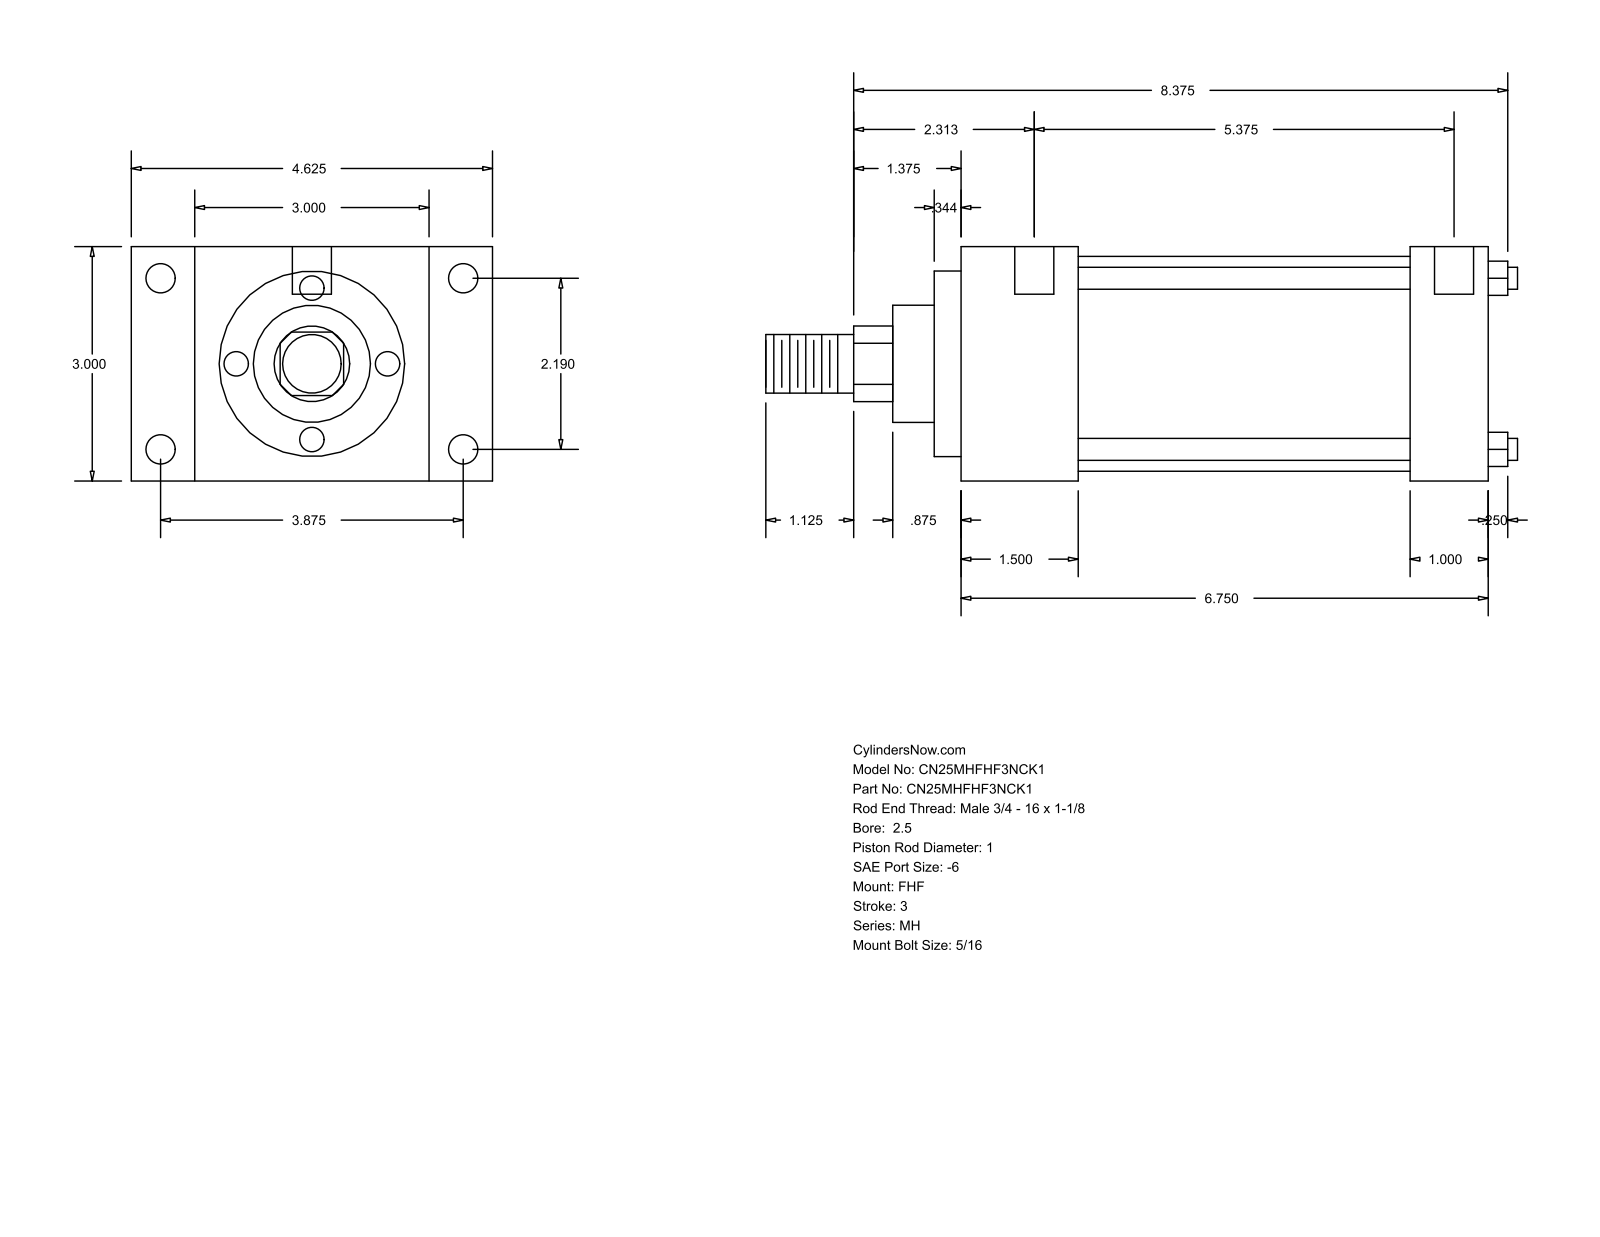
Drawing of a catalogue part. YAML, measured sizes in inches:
part_name: "MH_FHF__0250_1"
step_written_by: "GSSL Pune (CONFIG_CONTROL_DESIGN)"
units: inches
bodies: {solids: 0, faces: 90, planar: 61, cylindrical: 29, other: 0}
overall_size: [9.625, 4.625, 3]
round_holes:
  - {diameter: 0.219, count: 4}
  - {diameter: 0.375, count: 4}
  - {diameter: 0.5, count: 2}
round_bosses_or_shafts:
  - {diameter: 0.281, count: 4}
  - {diameter: 2.75, count: 1}
  - {diameter: 2.375, count: 1}
  - {diameter: 1.5, count: 1}
  - {diameter: 1, count: 1}
  - {diameter: 0.75, count: 1}
partial_cylinders:
  - {radius: 0.484, count: 1}
face_to_face_distances: [3, 6.75, 1.5, 5.25, 0.813, 3.813, 4.625, 5.75, 4.25, 1]
hole_center_spacings: [2.19, 3.875, 4.451, 5.687, 0.125, 0.187, 5.375, 5.5]
